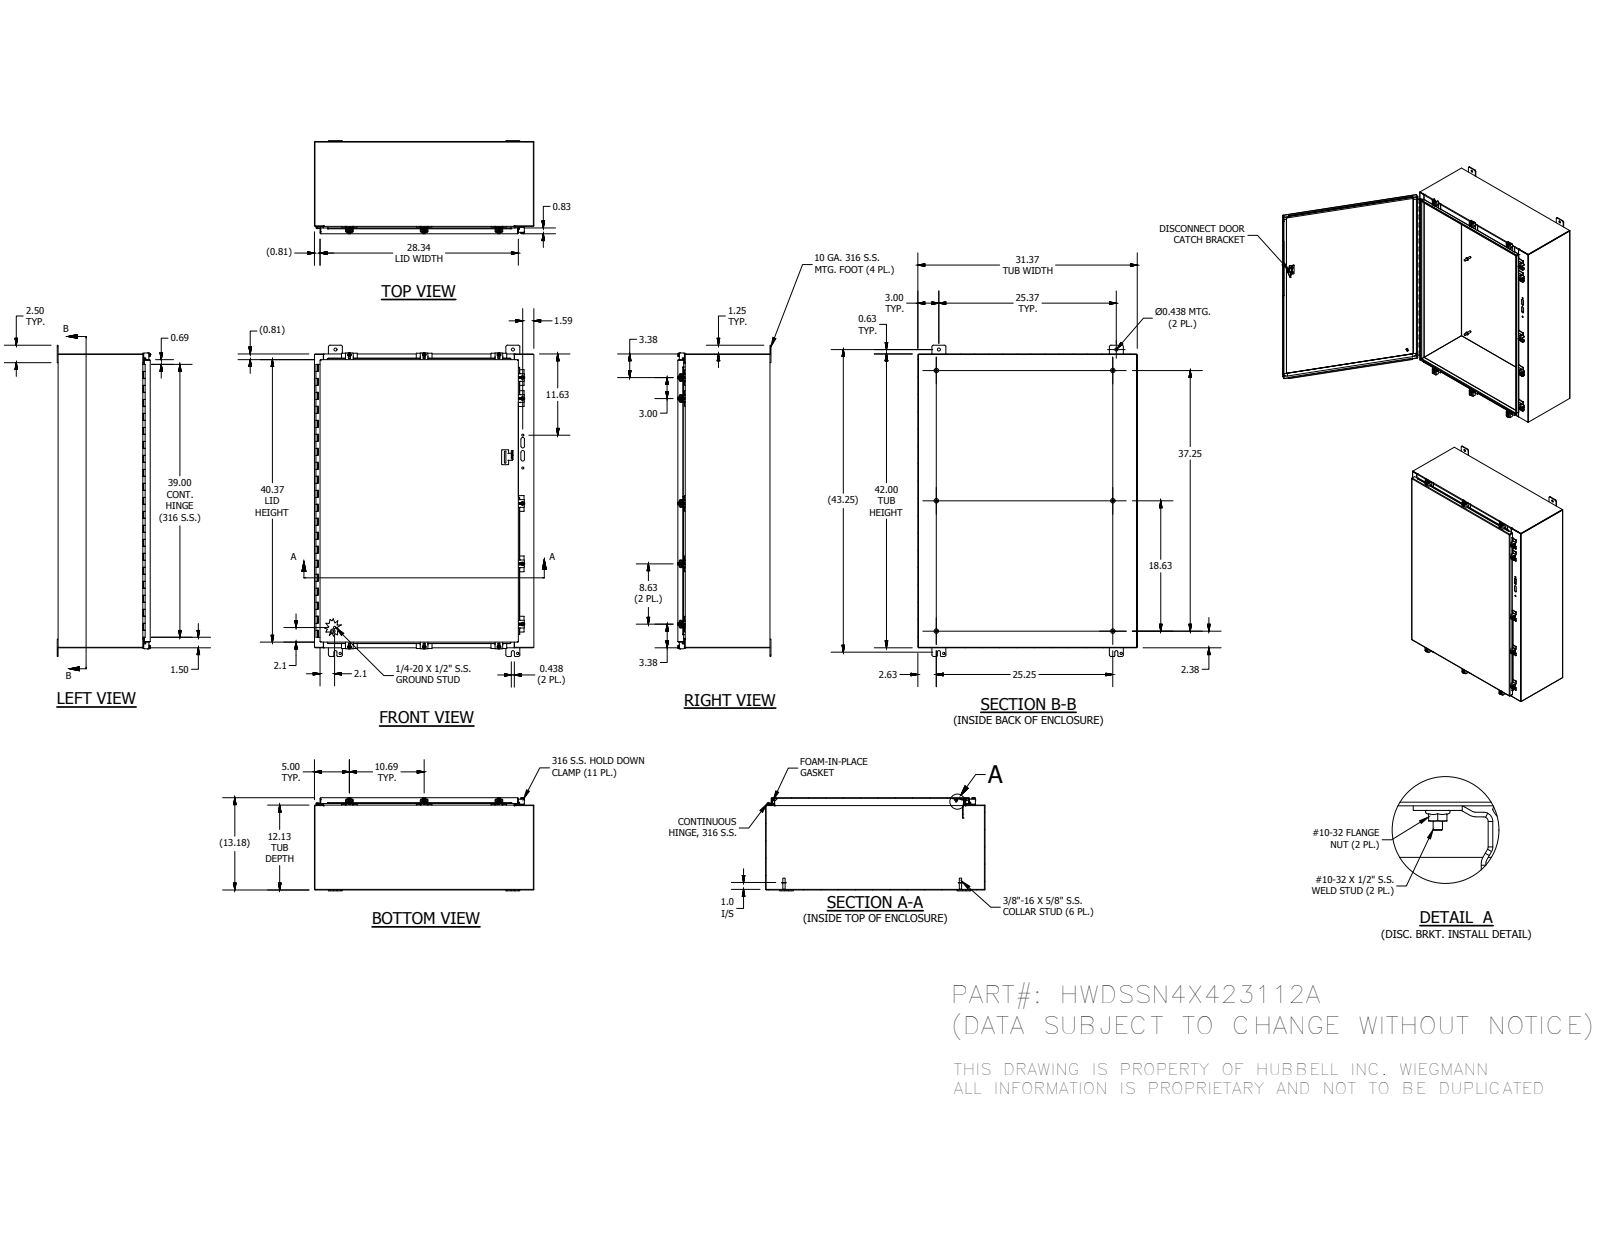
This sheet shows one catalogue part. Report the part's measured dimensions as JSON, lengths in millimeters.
{"part_name": "SSN4X423112ABLR; 38859; 34839; SSN4X4231ALID (+8 more)", "step_written_by": "Autodesk Inventor 2016 (AUTOMOTIVE_DESIGN)", "units": "millimeters", "bodies": {"solids": 24, "faces": 920, "planar": 569, "cylindrical": 283, "other": 68}, "overall_size": [1130.3, 796.92, 337.85], "volume_mm3": 6197000, "surface_area_mm2": 6379000, "round_holes": [[7.95, 4], [11.13, 4], [3.96, 2], [7.14, 2], [3.17, 1]], "round_bosses_or_shafts": [[15.88, 6], [8.38, 6], [8.56, 3], [6.35, 2], [4.83, 2], [3.05, 1]], "partial_cylinders_radius": [[0.79, 25], [2.67, 21], [6.35, 21], [3.17, 11], [0.25, 8], [1.92, 8], [2.38, 5], [4.76, 5]], "face_to_face_distances": [1.88, 332.79, 330.91, 334.67, 1064.92, 1.87, 793.17, 795.04, 795.05, 796.92], "hole_center_spacings": [40.46, 644.52, 1066.8, 1246.38, 628.13, 662.98, 1030.45, 1103.44]}
